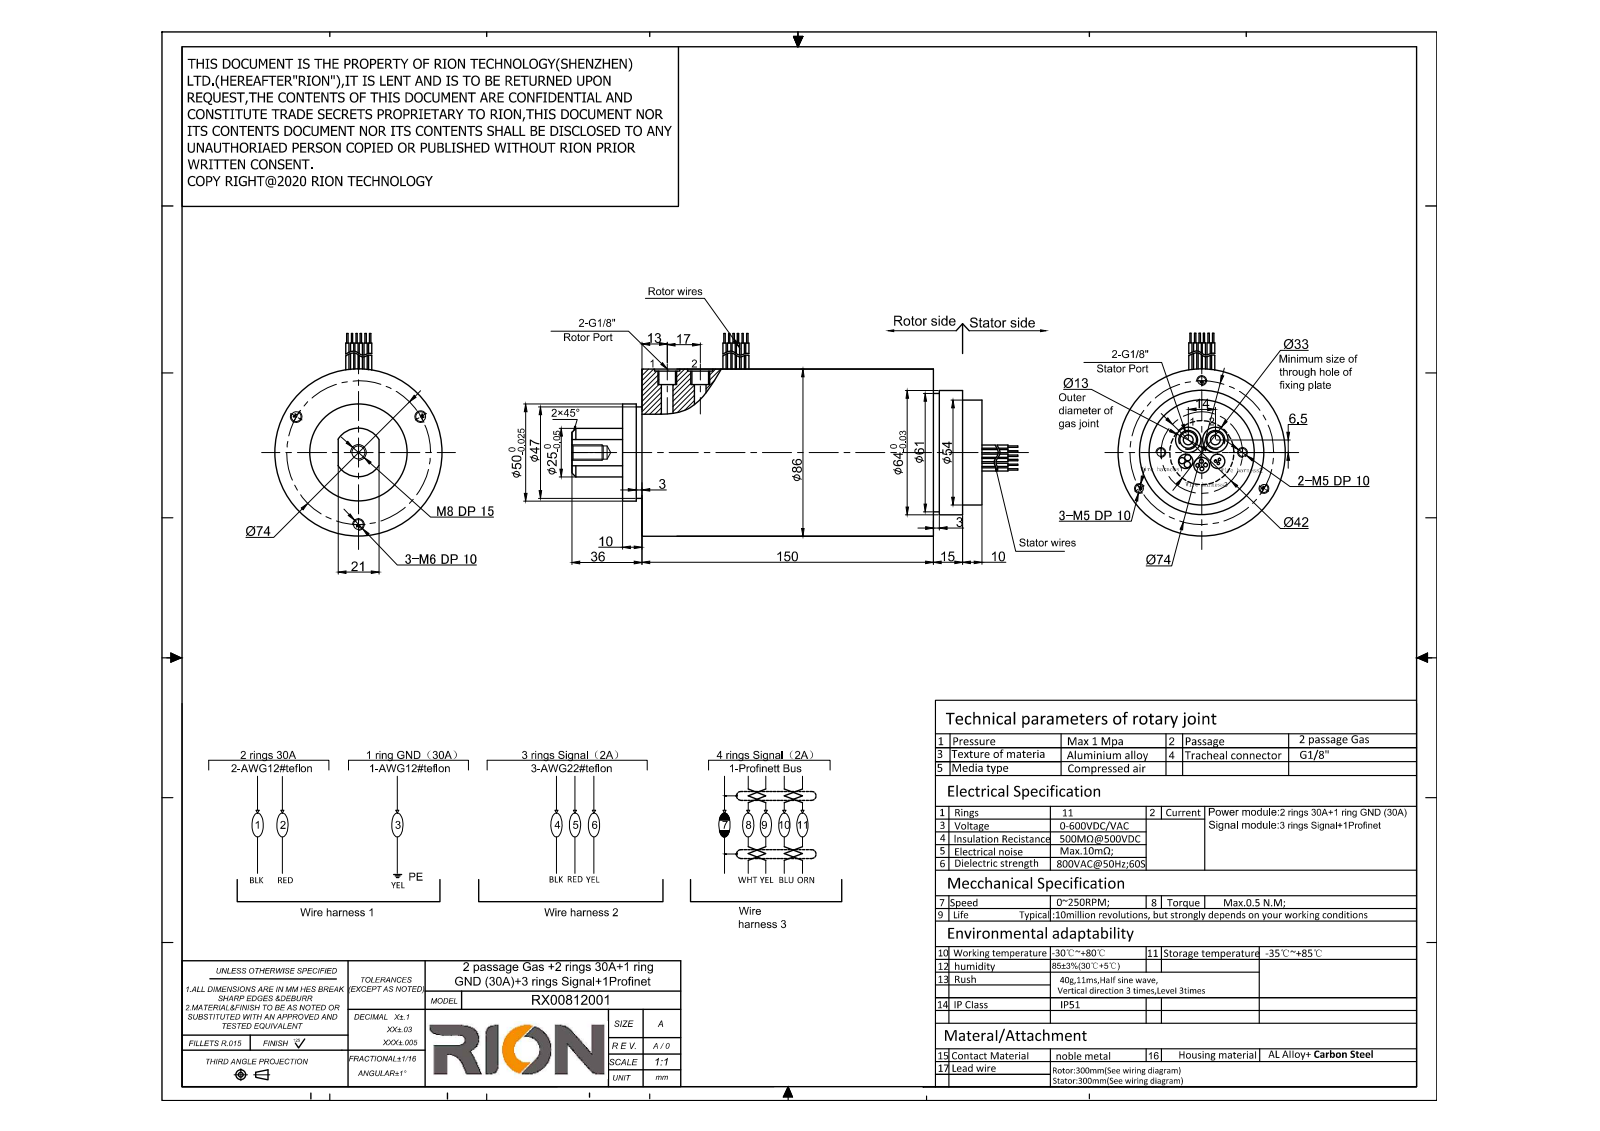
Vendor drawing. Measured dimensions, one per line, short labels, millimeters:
name: RX00812001--REPH200-P0330-S03-PROFINET
written by: SolidWorks 2014 (AUTOMOTIVE_DESIGN)
unit: mm
bodies: 1 solid, 142 faces (38 planar, 78 cylindrical, 26 other)
size: 231 × 105.7 × 86
volume: 969 534 mm³; area: 66 829 mm²
holes: 5× ⌀4.2, 5× ⌀5, 4× ⌀8.8, 2× ⌀7.5, 1× ⌀7, 1× ⌀8
bosses: 6× ⌀3.2, 6× ⌀1.3, 2× ⌀6, 1× ⌀86, 1× ⌀64, 1× ⌀61, 1× ⌀54, 1× ⌀50
rounds: 1× R12.5
face distances: 175, 150, 10, 25, 160, 185, 165, 15, 3, 153
hole spacings: 37, 64.08, 21.54, 42.54, 56.17, 0.55, 8.49, 9
